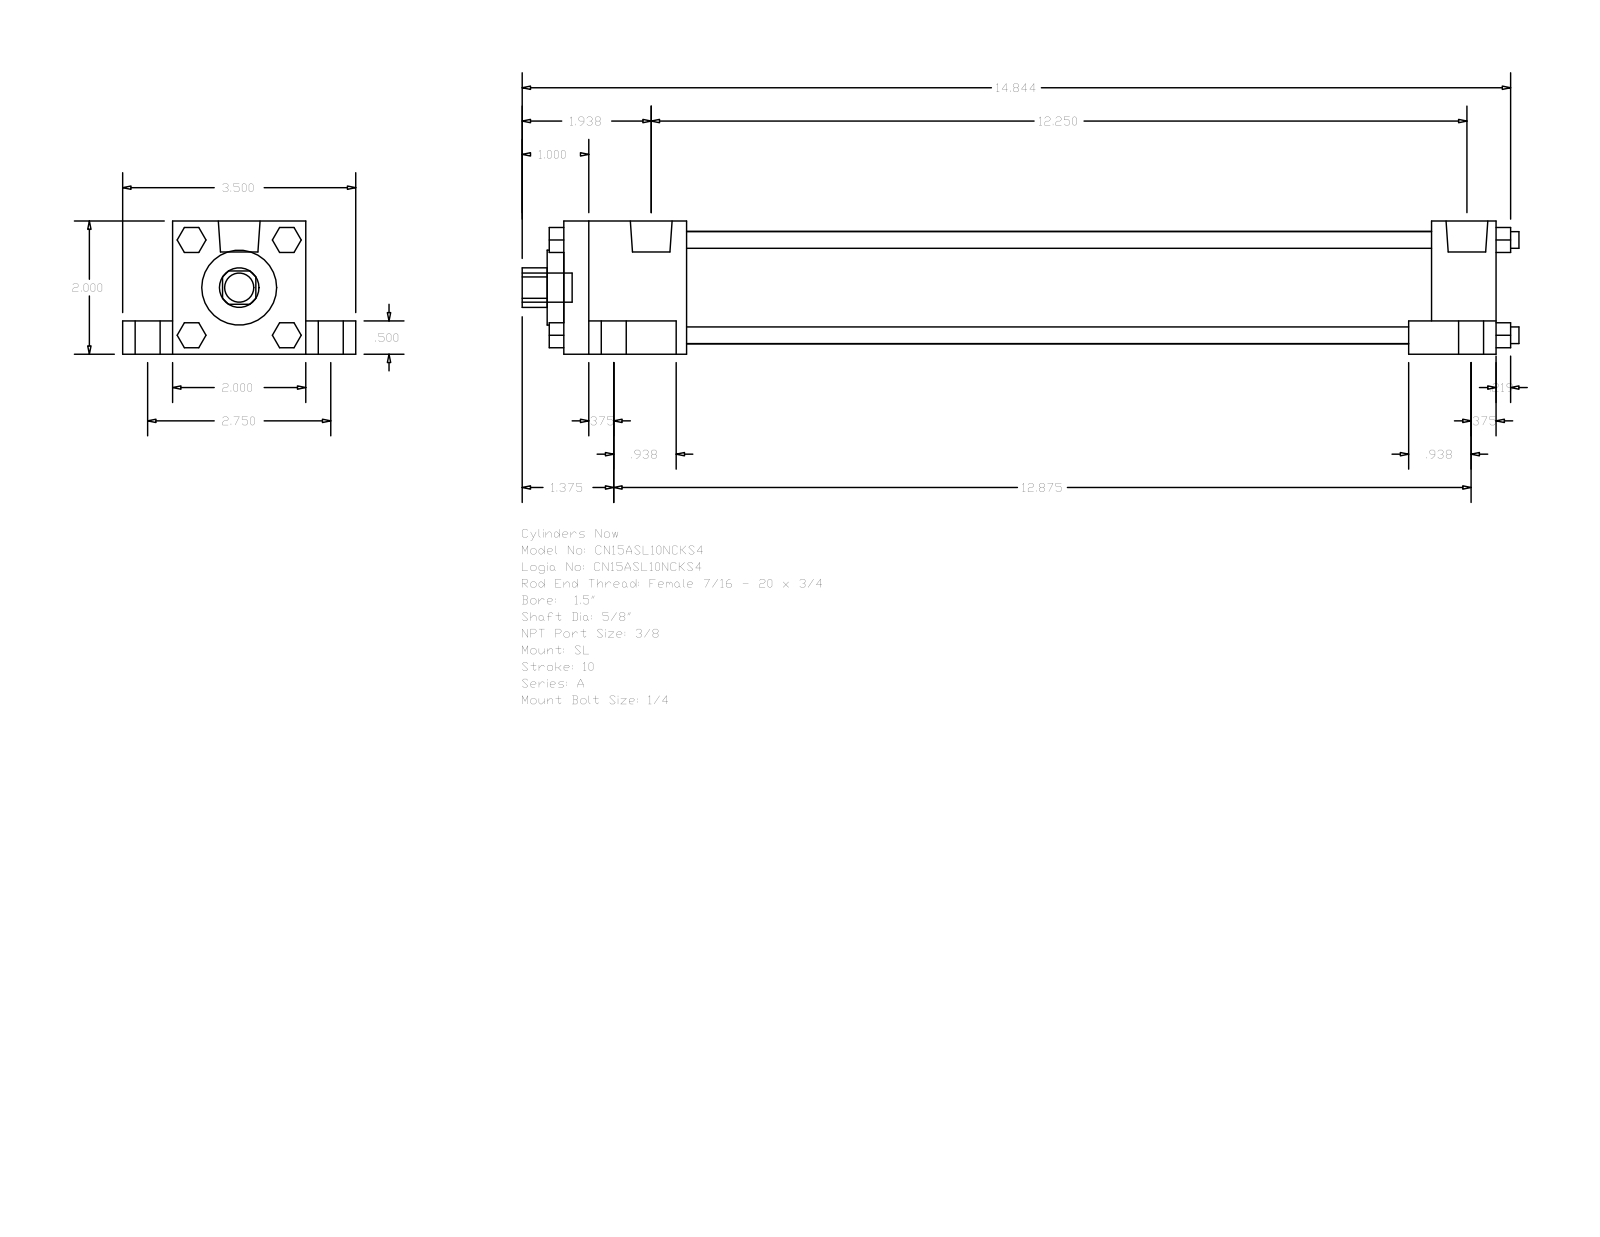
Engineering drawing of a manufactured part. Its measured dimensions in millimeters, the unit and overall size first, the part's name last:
Units: millimetres
Overall size (bounding box): 380.21 × 88.9 × 50.8
Round holes (diameter × count): ⌀15.88 ×1, ⌀28.57 ×1, ⌀42.93 ×1
Round bosses / shafts (diameter × count): ⌀15.88 ×4, ⌀9.53 ×4, ⌀6.35 ×4, ⌀5.56 ×4, ⌀15.93 ×2, ⌀11.11 ×1
Partial cylindrical surfaces — rounded edges, fillets, slot ends (radius × count): R7.54 ×1
Main face-to-face distances: 50.8, 19.05, 12.7, 38.1, 69.85, 355.6, 9.52, 33.34, 330.99, 24.61
Bodies: 0 solids, 148 faces (112 planar, 36 cylindrical, 0 other)
Part name (STEP PRODUCT): A_SL__0150_0.625
STEP written by: GSSL Pune (CONFIG_CONTROL_DESIGN)
